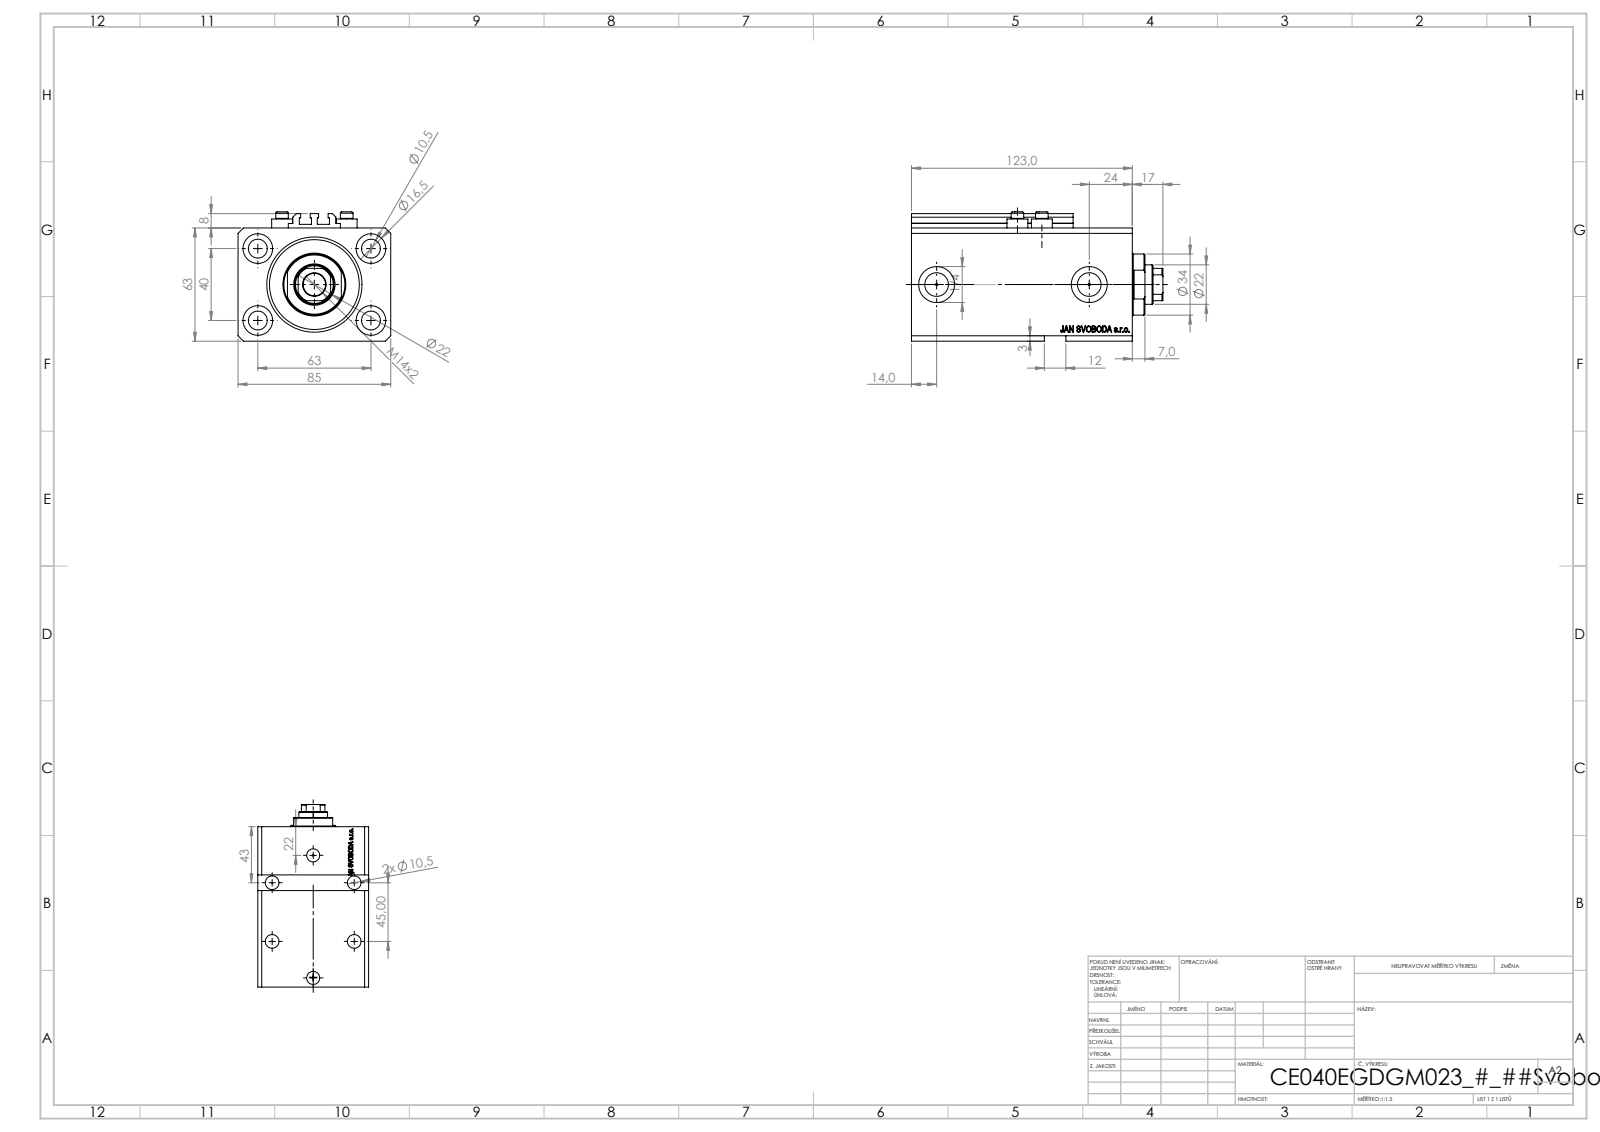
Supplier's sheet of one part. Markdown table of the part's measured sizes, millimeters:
| quantity | value |
| --- | --- |
| part name | V250CE_C_VCP; V250CE_E_Body; ALLEN BOLT V250CE; V250CE_VC_E |
| STEP written by | SolidWorks 2019 (CONFIG_CONTROL_DESIGN) |
| units | millimeters |
| bodies | 8 solids, 1123 faces (539 planar, 158 cylindrical, 426 other) |
| overall size | 140 × 85 × 72 |
| volume | 553 016 mm³ |
| surface area | 120 484 mm² |
| round holes (diameter × count) | 10.5 × 8, 1.25 × 4, 4 × 4, 16.5 × 4, 10 × 2, 13.16 × 2, 20 × 2, 12.5 × 1, 22 × 1, 40 × 1, 53 × 1 |
| round bosses / shafts (diameter × count) | 11.6 × 4, 7 × 4, 34 × 1 |
| partial cylindrical surfaces (radius × count) | 0.2 × 10, 10.5 × 1 |
| main face-to-face distances | 63, 85, 123, 17, 106, 11.4, 94.6, 111.6, 3, 56 |
| hole center spacings | 37.31, 63, 13.6, 15.4, 24.96, 27.54, 33.62, 36 |
